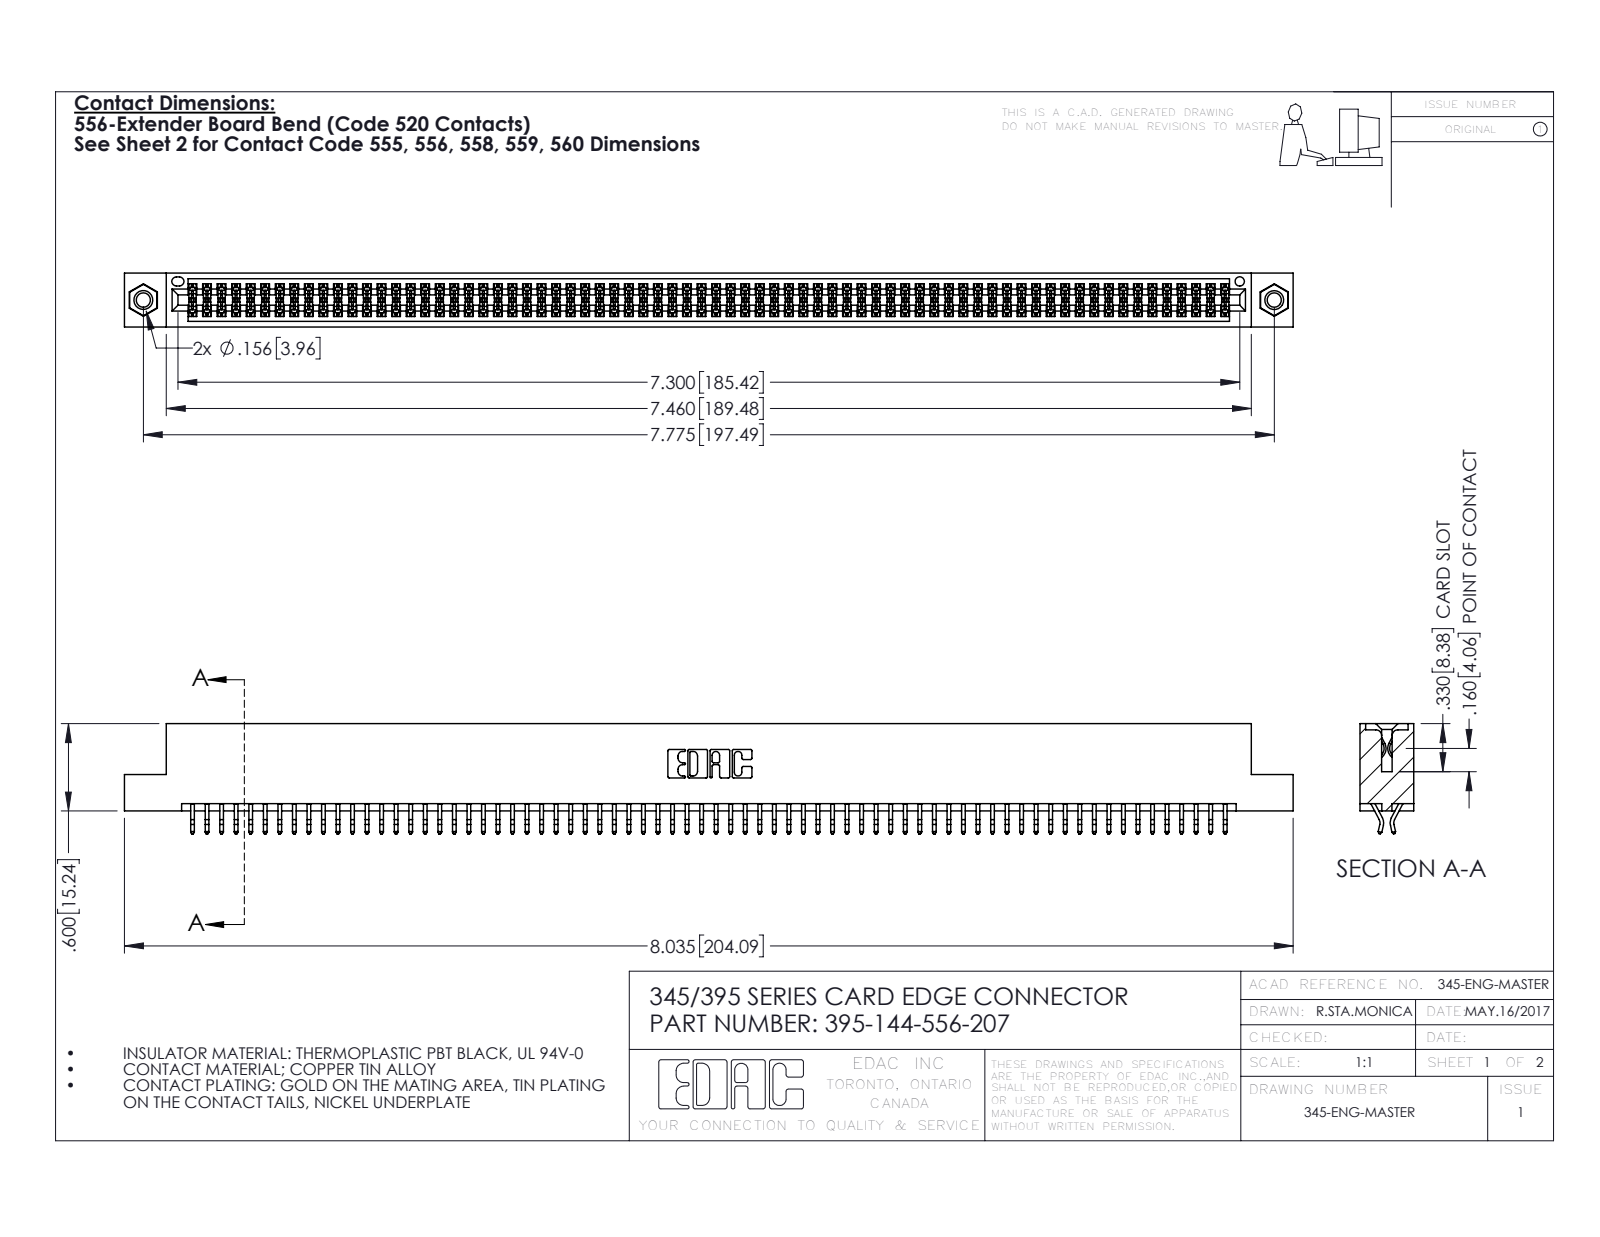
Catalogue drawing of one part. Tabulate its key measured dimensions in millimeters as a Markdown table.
| quantity | value |
| --- | --- |
| part name | 395-144-556-207; 345 Part_Flush Mounting Lugs - 0.156 Dia-TI; 345-250-001_345-250-005-103; 345-292-001_556 Tail |
| STEP written by | SolidWorks 2016 (CONFIG_CONTROL_DESIGN) |
| units | millimeters |
| bodies | 147 solids, 8250 faces (5440 planar, 2794 cylindrical, 16 other) |
| overall size | 204.1 × 19.2 × 9.4 |
| volume | 20 090 mm³ |
| surface area | 30 170 mm² |
| round holes (diameter × count) | 2.5 × 2, 3.2 × 2, 4 × 2, 1.6 × 1 |
| round bosses / shafts (diameter × count) | 3.9 × 2 |
| partial cylindrical surfaces (radius × count) | 0.2 × 216, 0.3 × 22, 0.2 × 6, 0.8 × 6, 0.7 × 3, 0.3 × 2, 0.4 × 2, 0.5 × 2 |
| main face-to-face distances | 1.8, 7.6, 9.4, 5.1, 0.6, 2.5, 6.9, 5.7, 4.4, 3.8 |
| hole center spacings | 6.9, 191.5, 197.5 |
